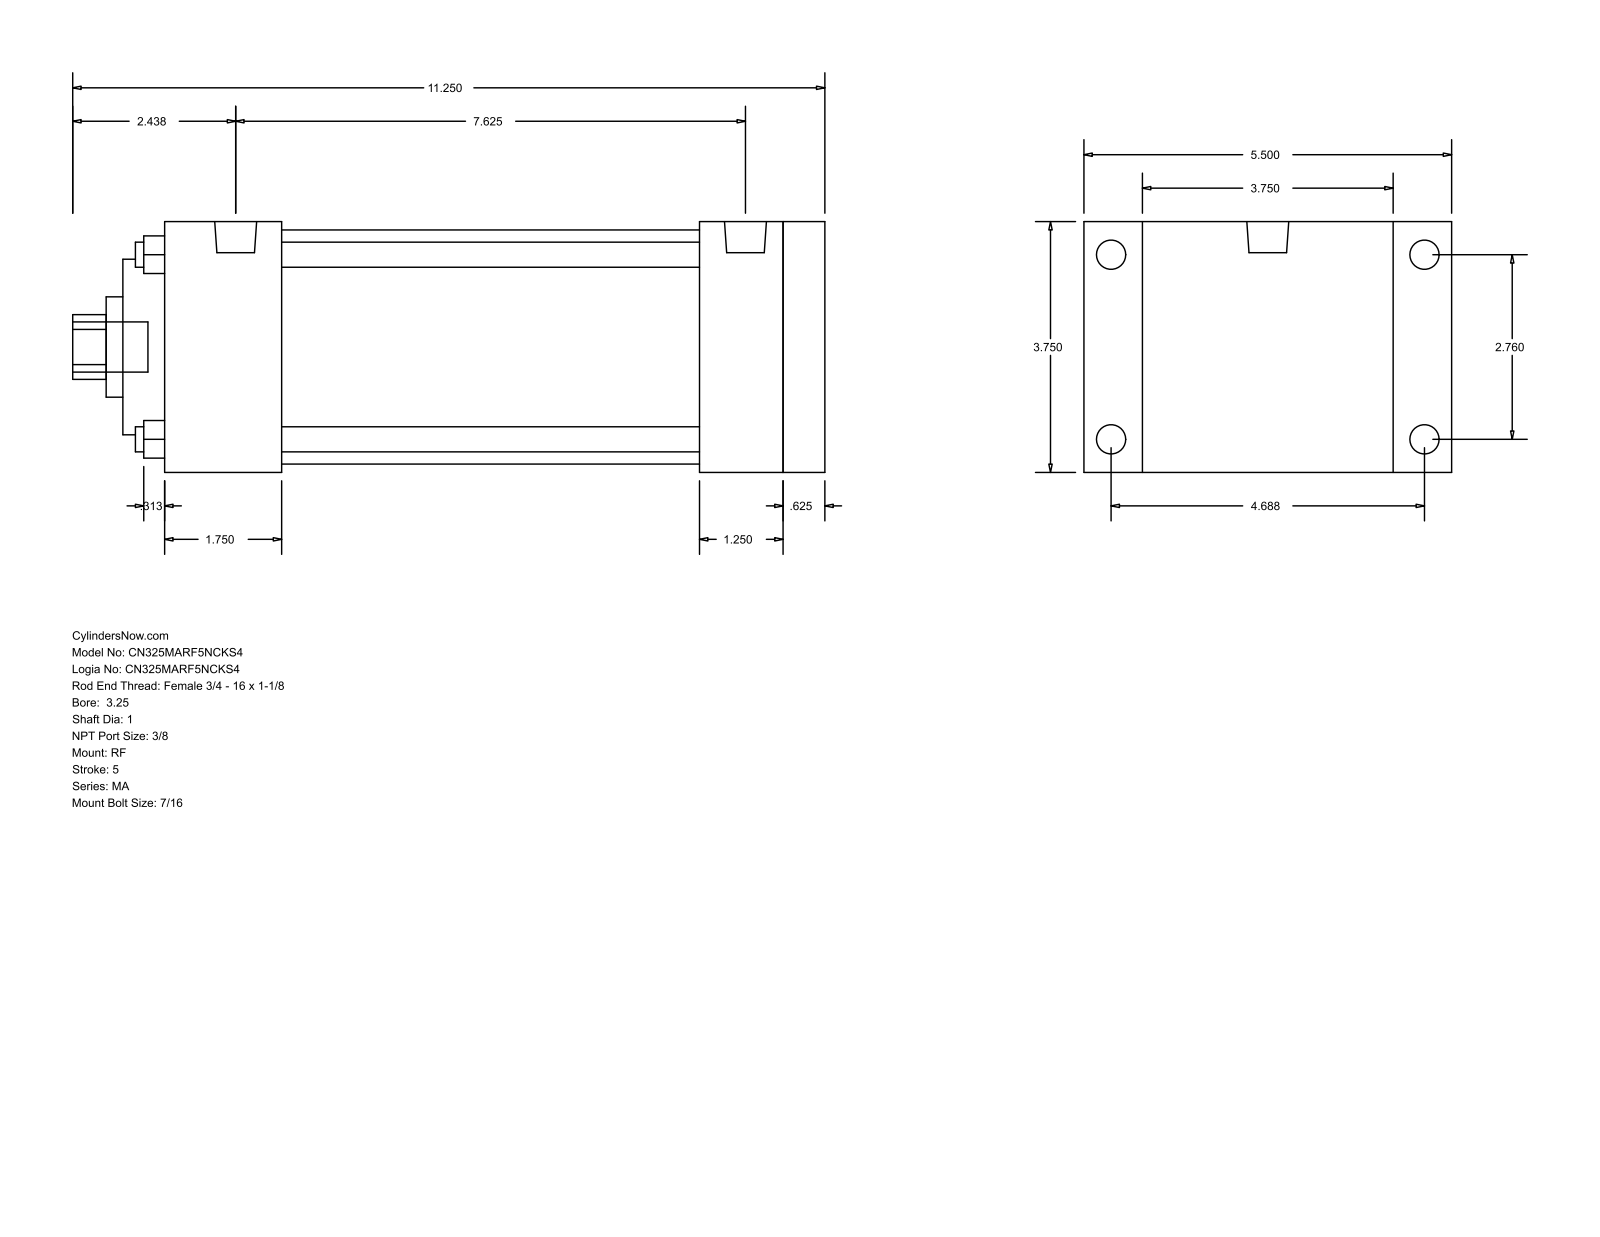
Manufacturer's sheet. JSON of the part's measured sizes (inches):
{"part_name": "MA_RF__0325_1", "step_written_by": "GSSL Pune (CONFIG_CONTROL_DESIGN)", "units": "inches", "bodies": {"solids": 0, "faces": 94, "planar": 65, "cylindrical": 29, "other": 0}, "overall_size": [11.25, 5.5, 3.75], "round_holes": [[0.375, 4], [1, 1], [1.5, 1], [2.625, 1], [3.5, 1]], "round_bosses_or_shafts": [[0.437, 8], [0.627, 2], [0.75, 1]], "partial_cylinders_radius": [[0.484, 1]], "face_to_face_distances": [3.75, 9.875, 0.625, 9.25, 0.875, 4.625, 8, 1.25, 1.875, 1.75], "hole_center_spacings": [1.952, 2.76, 3.903]}
